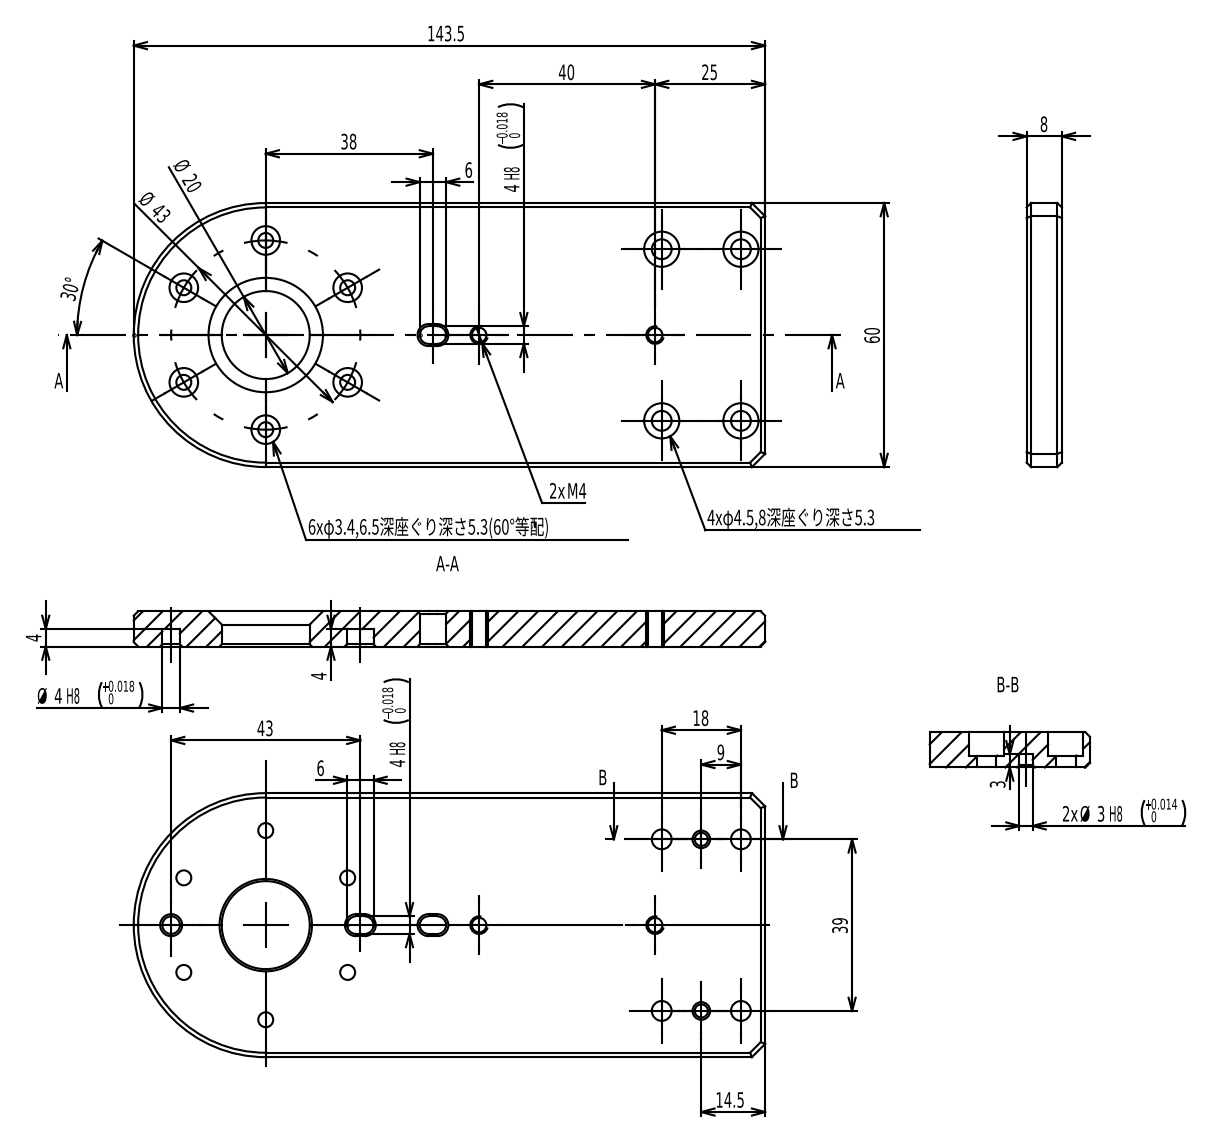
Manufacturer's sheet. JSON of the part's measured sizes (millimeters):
{"part_name": "PDG60-2", "step_written_by": "SolidWorks 2020 (CONFIG_CONTROL_DESIGN)", "units": "millimeters", "bodies": {"solids": 1, "faces": 122, "planar": 41, "cylindrical": 59, "other": 22}, "overall_size": [143.5, 60, 8], "volume_mm3": 59583, "surface_area_mm2": 20410, "round_holes": [[3.4, 6], [6.5, 6], [4.5, 4], [8, 4], [3, 2], [3.3, 2], [4, 1], [20, 1]], "partial_cylinders_radius": [[2, 4], [30, 1]], "face_to_face_distances": [8, 60, 46.66, 5.3, 2.7, 4, 28, 32, 1.3, 5], "hole_center_spacings": [21.5, 37.24, 9, 40.02, 39, 43, 11.13, 18]}
